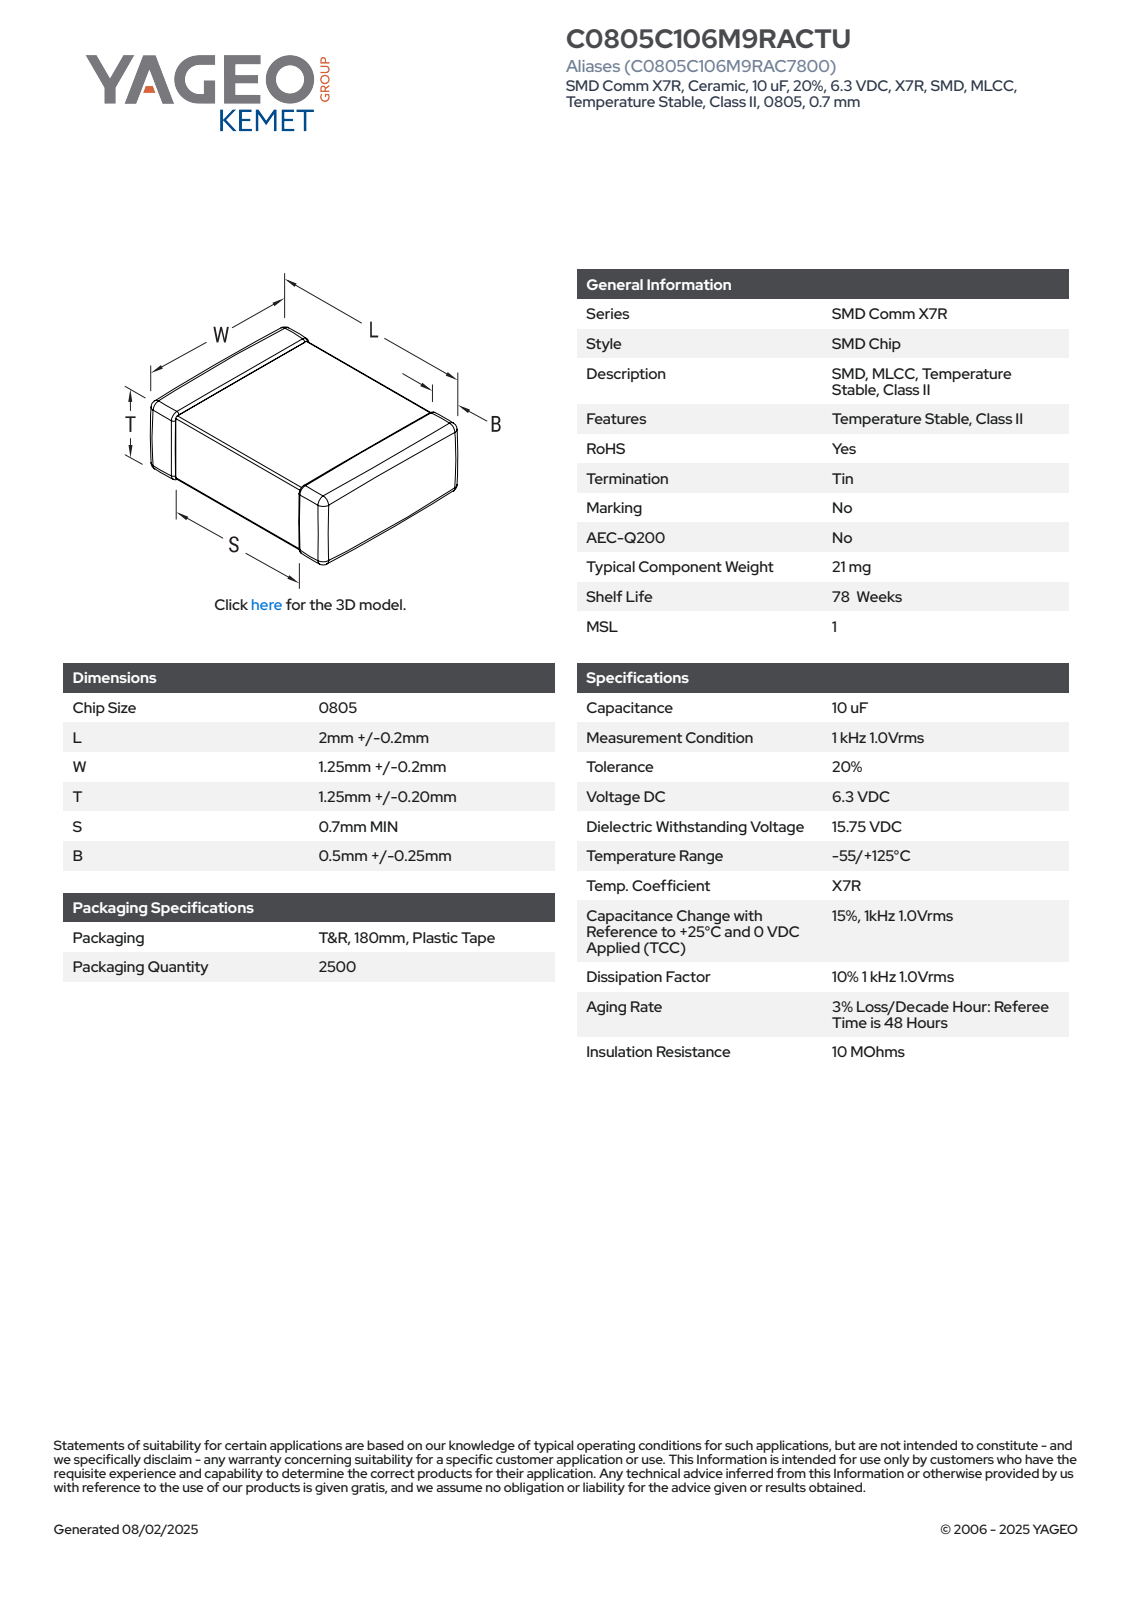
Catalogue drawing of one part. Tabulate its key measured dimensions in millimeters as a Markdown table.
| quantity | value |
| --- | --- |
| part name | CCS_CCSTD_0805_L2.2W1.45T1.45B0.5 |
| STEP written by | SolidWorks 2021 (AUTOMOTIVE_DESIGN) |
| units | millimeters |
| bodies | 4 solids, 125 faces (71 planar, 38 cylindrical, 16 other) |
| overall size | 2.2 × 1.45 × 1.45 |
| volume | 4 mm³ |
| surface area | 17 mm² |
| main face-to-face distances | 1.42, 1.45, 2.2, 1.39, 0.97, 1.23, 1.19, 1.01, 0.58, 0.87 |
